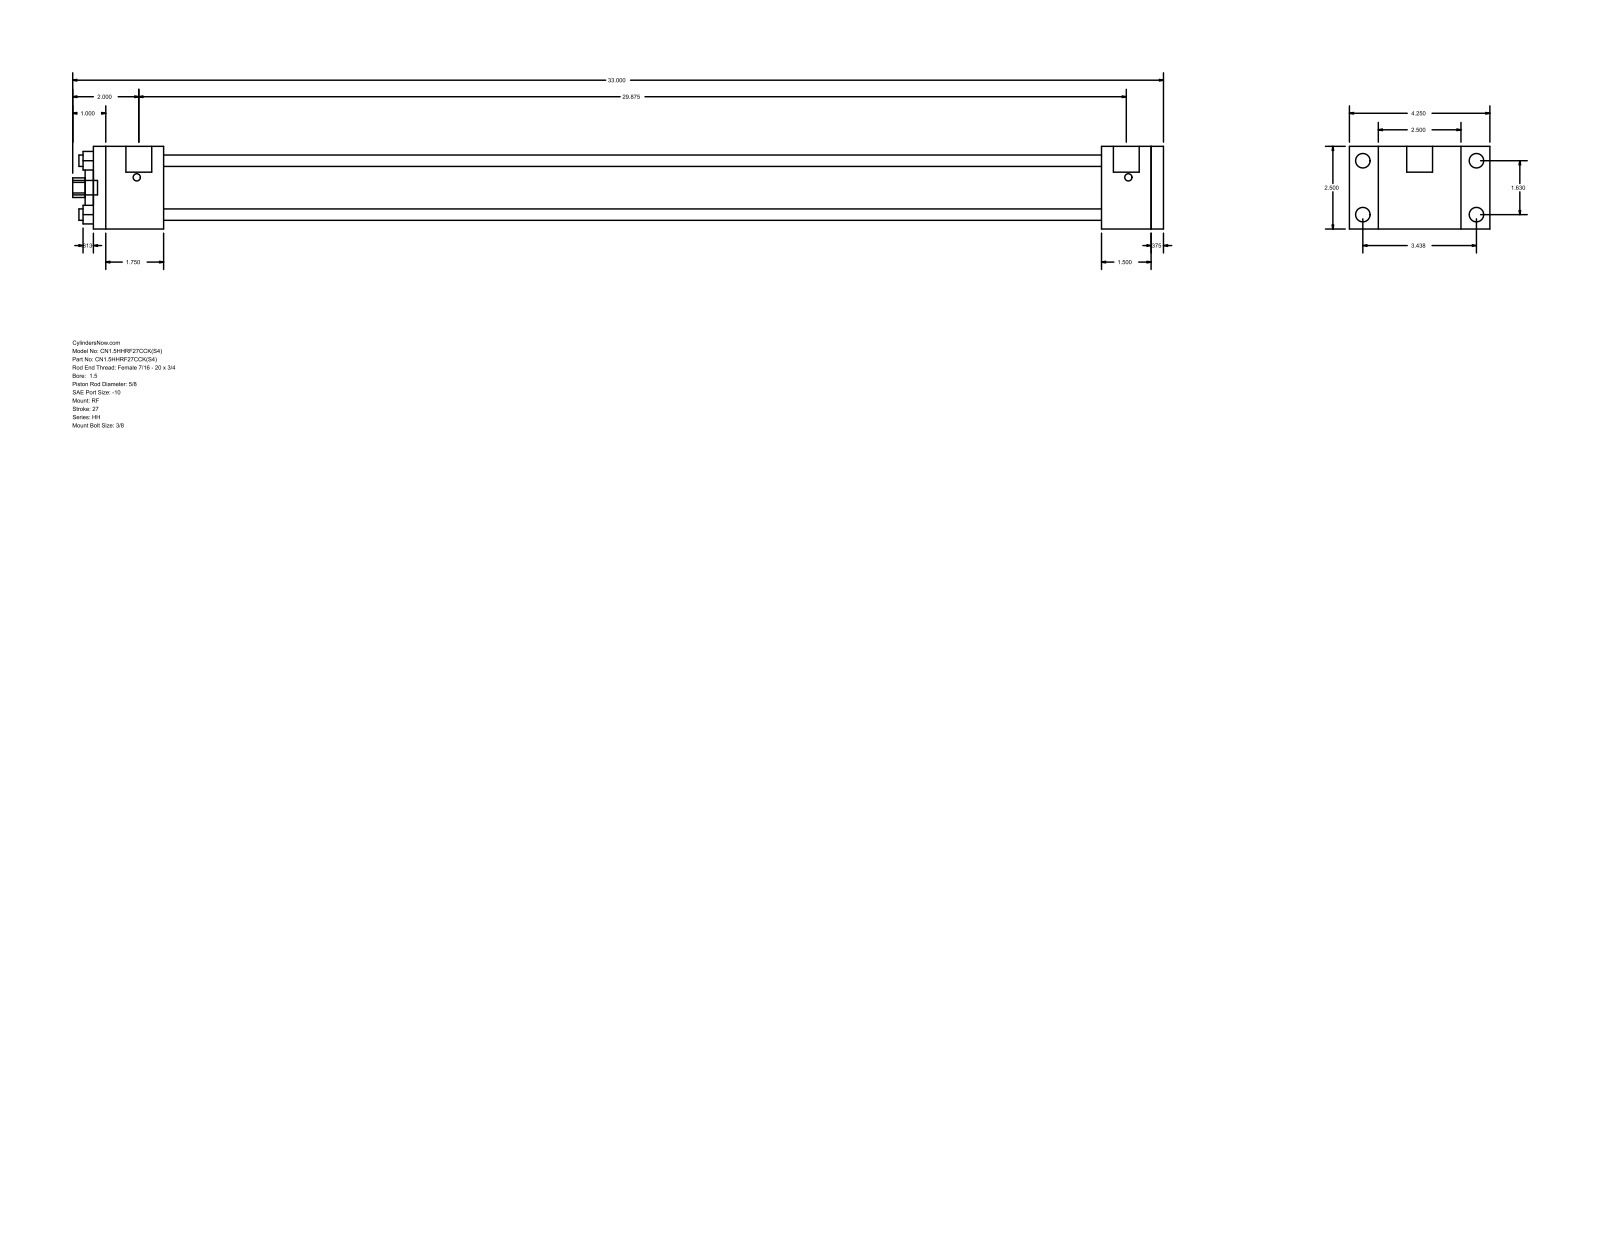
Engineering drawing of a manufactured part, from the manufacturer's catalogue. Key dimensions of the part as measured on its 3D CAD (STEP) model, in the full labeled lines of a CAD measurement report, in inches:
Part name (STEP PRODUCT): HH_RF__0150_0.625
STEP written by: GSSL Pune (CONFIG_CONTROL_DESIGN)
Units: inches
Bodies: 0 solids, 92 faces (64 planar, 28 cylindrical, 0 other)
Overall size (bounding box): 33 × 4.25 × 2.5
Round holes (diameter × count): ⌀0.345 ×4, ⌀0.625 ×1, ⌀1.125 ×1, ⌀1.75 ×1
Round bosses / shafts (diameter × count): ⌀0.438 ×4, ⌀0.219 ×4, ⌀0.781 ×2, ⌀0.437 ×1
Partial cylindrical surfaces — rounded edges, fillets, slot ends (radius × count): R0.297 ×1
Main face-to-face distances: 2.5, 32.375, 0.375, 32, 2.125, 30.5, 28.375, 29.875, 30.25, 1.5
Hole centre spacings: 1.152, 1.63, 2.305
